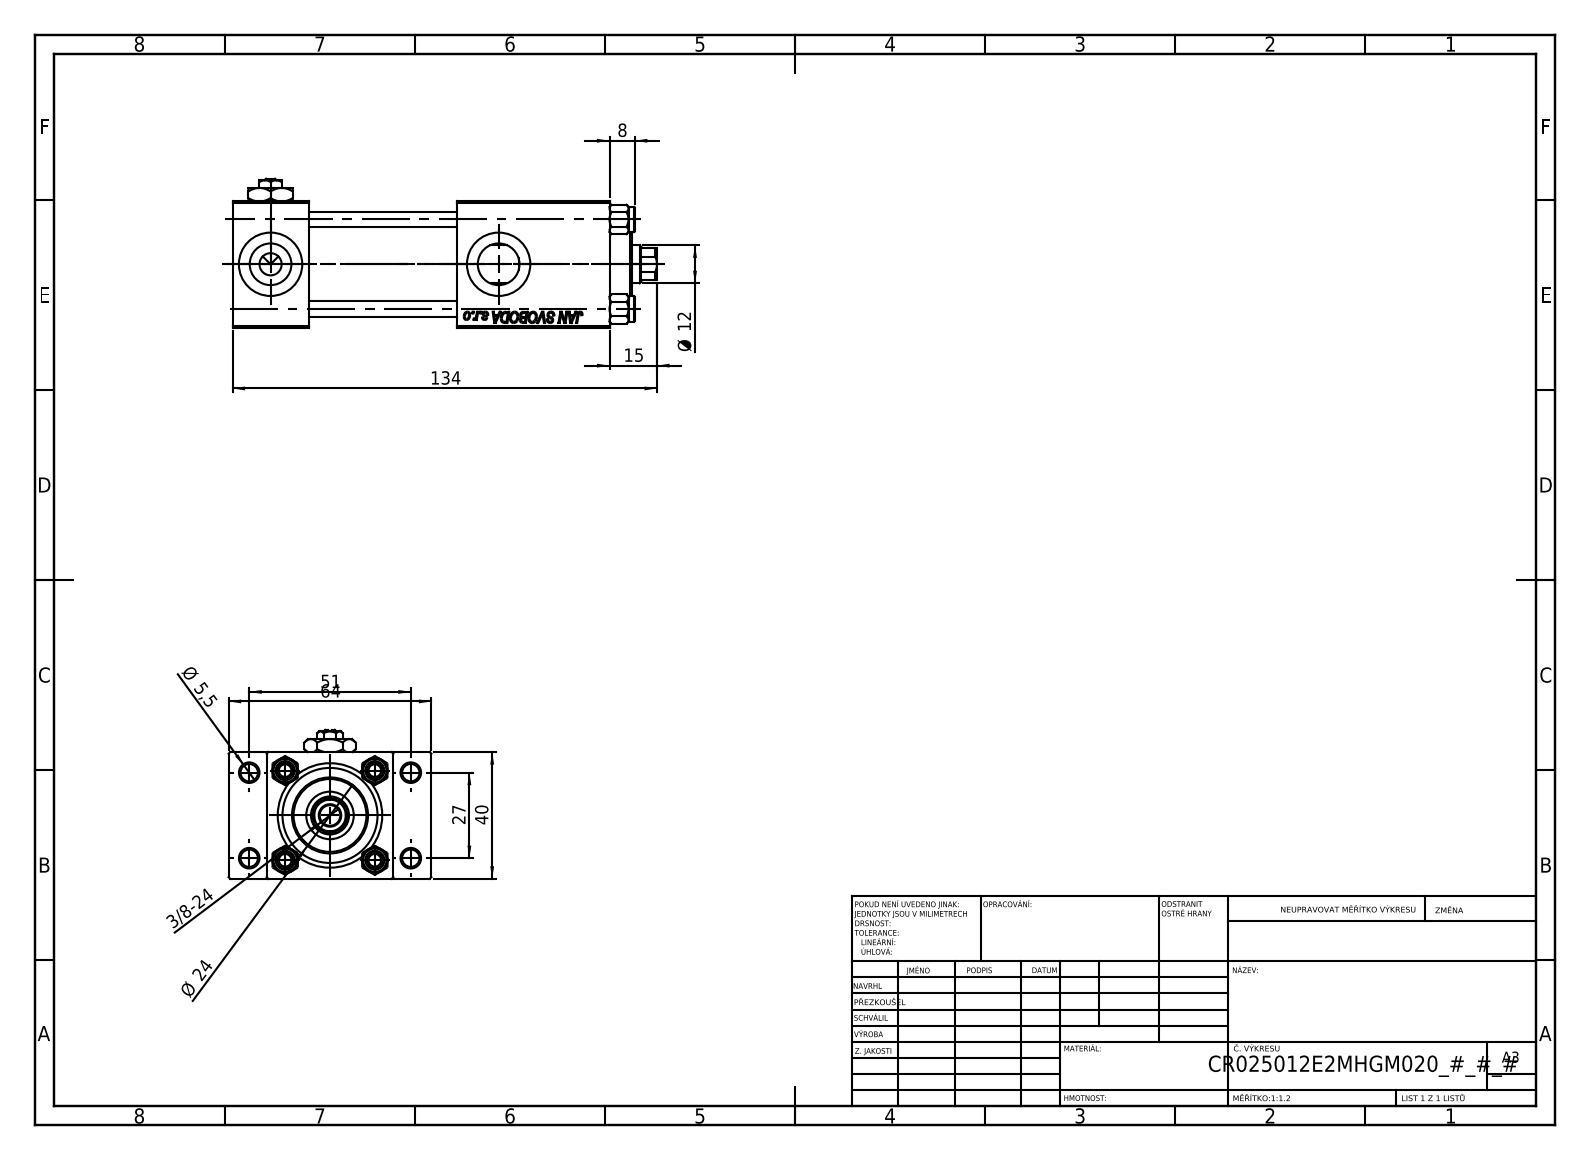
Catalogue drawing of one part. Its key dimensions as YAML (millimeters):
part_name: "V215_VC_A; Zatka_pro_OIL_PORT; NUT_M5_E; V215CR_VCP_E (+2 more)"
step_written_by: "SolidWorks 2019 (CONFIG_CONTROL_DESIGN)"
units: millimeters
bodies: {solids: 12, faces: 1187, planar: 520, cylindrical: 93, other: 574}
overall_size: [134, 64, 47]
volume: 162456
surface_area: 63452
round_holes:
  - {diameter: 5, count: 4}
  - {diameter: 5.5, count: 4}
  - {diameter: 20, count: 4}
  - {diameter: 7, count: 3}
  - {diameter: 13.16, count: 3}
  - {diameter: 6.5, count: 1}
  - {diameter: 12, count: 1}
  - {diameter: 15, count: 1}
  - {diameter: 25, count: 1}
  - {diameter: 30, count: 1}
round_bosses_or_shafts:
  - {diameter: 8, count: 4}
  - {diameter: 31, count: 1}
  - {diameter: 24, count: 1}
partial_cylinders:
  - {radius: 5.5, count: 1}
face_to_face_distances: [40, 24, 12, 52, 119, 95, 90.3, 66.3, 28.7, 47]
hole_center_spacings: [11.37, 20.01, 28.3, 28.85, 29.89, 39.66, 48.34, 27]
